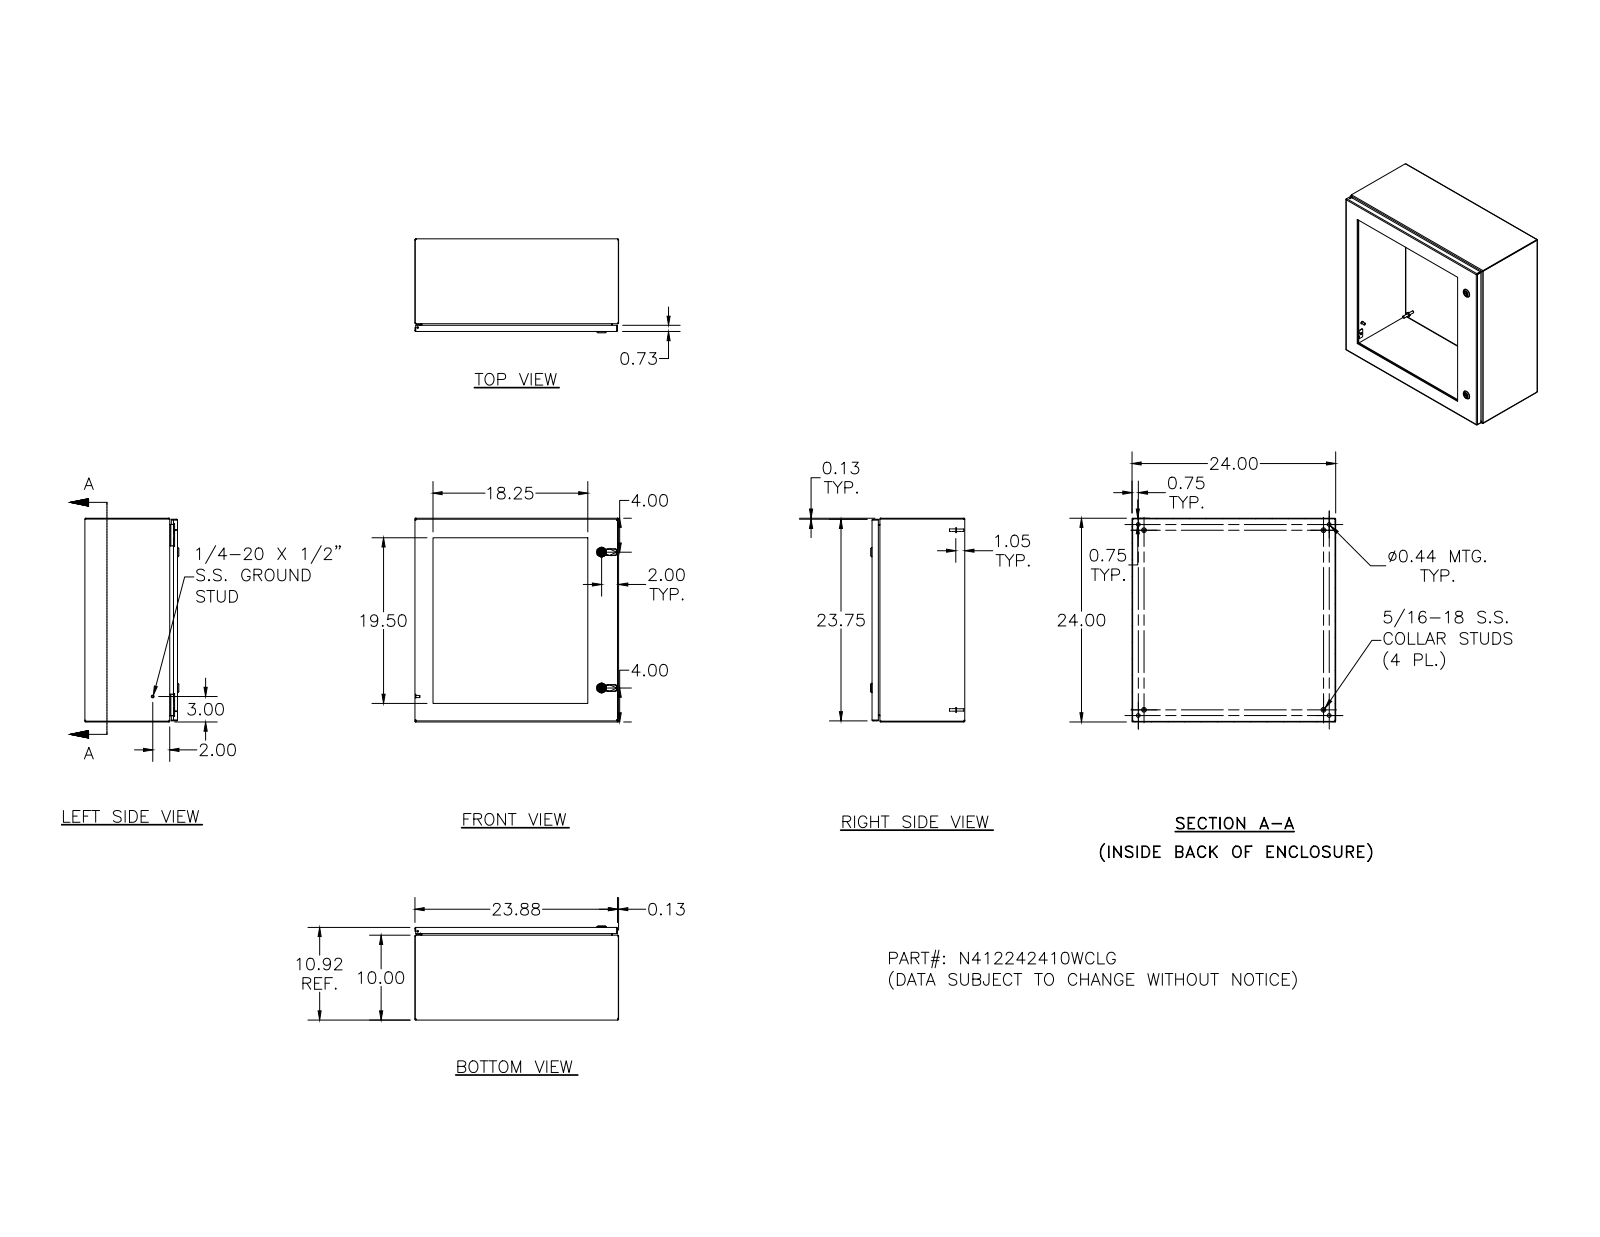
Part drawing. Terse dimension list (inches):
name: N412242410WCLG
written by: SolidWorks 2018 (AUTOMOTIVE_DESIGN)
unit: in
bodies: 84 solids, 2510 faces (971 planar, 762 cylindrical, 777 other)
size: 24 × 24 × 11.075
volume: 250.2 in³; area: 4 943 in²
holes: 22× ⌀0.156, 20× ⌀0.281, 5× ⌀0.188, 4× ⌀0.093, 4× ⌀0.152, 4× ⌀0.167, 4× ⌀0.172, 4× ⌀0.437, 2× ⌀0.197, 2× ⌀0.315, 2× ⌀0.394, 2× ⌀0.402
bosses: 20× ⌀0.337, 20× ⌀0.19, 10× ⌀0.25, 4× ⌀0.563, 4× ⌀0.36, 4× ⌀0.32, 4× ⌀0.3, 4× ⌀0.275
rounds: 54× R0.012, 34× R0.031, 26× R0.05, 24× R0.105, 23× R0.02, 18× R0.016, 16× R0.125, 8× R0.032
face distances: 0.074, 23.926, 10.843, 10.769, 24, 23.852, 0.25, 10.593, 10.519, 10.917
hole spacings: 4, 8, 21.132, 12, 20, 22.239, 20.75, 6.221
